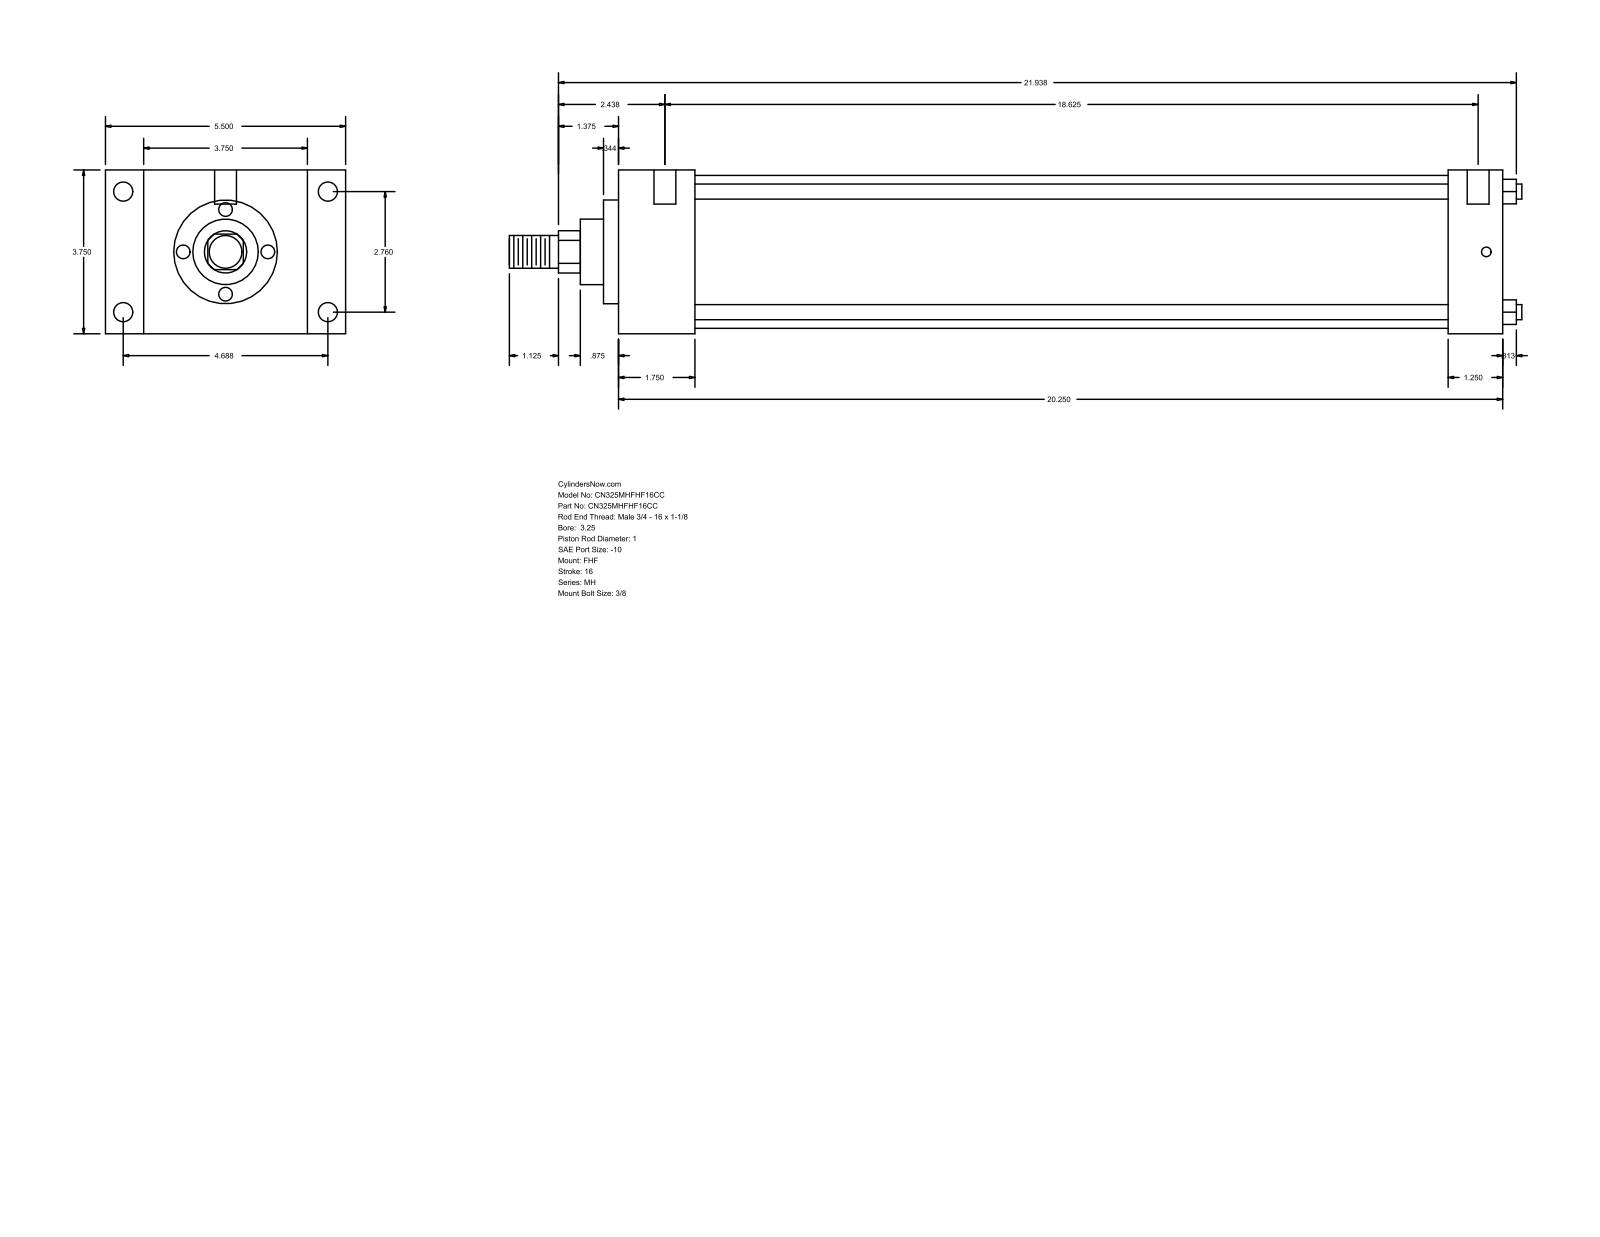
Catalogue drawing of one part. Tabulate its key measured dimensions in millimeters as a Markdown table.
| quantity | value |
| --- | --- |
| part name | MH_FHF__0325_1 |
| STEP written by | GSSL Pune (CONFIG_CONTROL_DESIGN) |
| units | millimeters |
| bodies | 0 solids, 90 faces (61 planar, 29 cylindrical, 0 other) |
| overall size | 588.96 × 139.7 × 95.25 |
| round holes (diameter × count) | 5.56 × 4, 11.13 × 4, 12.7 × 2 |
| round bosses / shafts (diameter × count) | 8.76 × 4, 88.9 × 1, 60.33 × 1, 38.1 × 1, 25.4 × 1, 19.05 × 1 |
| partial cylindrical surfaces (radius × count) | 12.29 × 1 |
| main face-to-face distances | 95.24, 514.35, 44.46, 469.89, 22.23, 117.47, 139.7, 482.6, 438.14, 31.75 |
| hole center spacings | 70.1, 119.06, 138.16, 479.42, 1.58, 4.76, 473.08, 474.66 |
